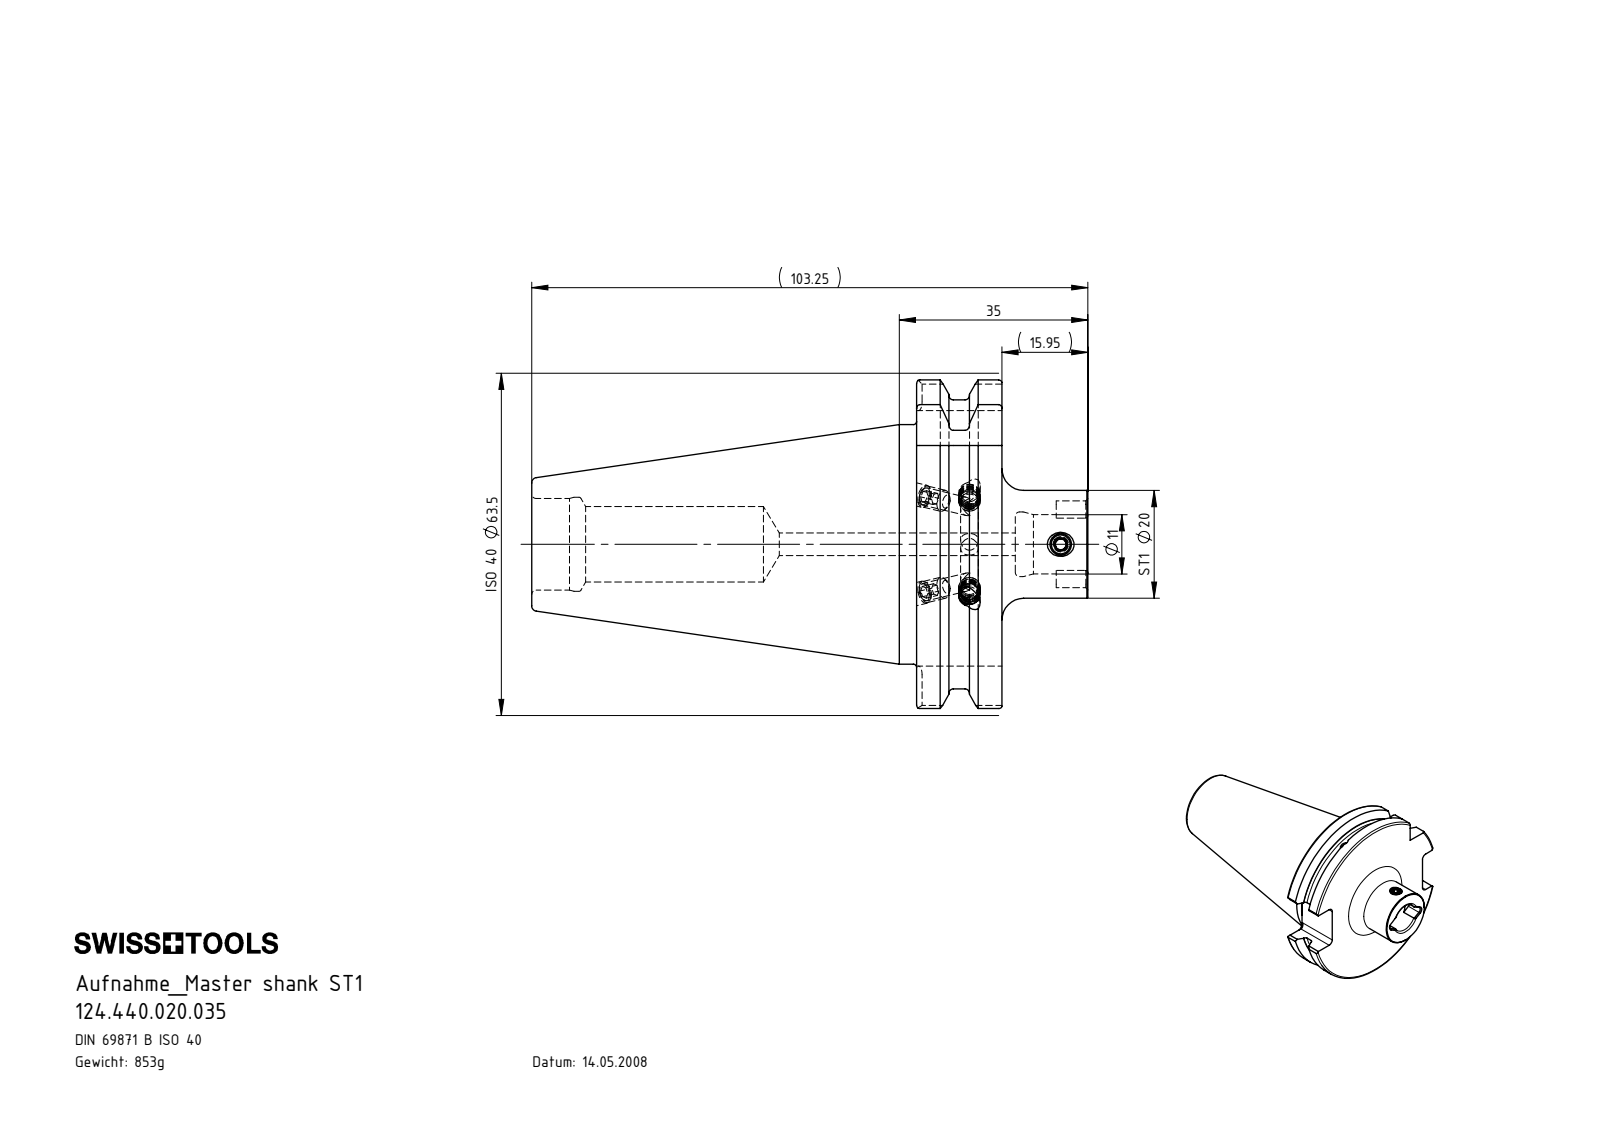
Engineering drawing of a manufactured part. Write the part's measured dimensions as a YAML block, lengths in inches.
part_name: "ISO 4026 - M4 x 5_PreviewCfg; SB4.ST1.K01.035; ST1-ER1.001.005_A; KVT_MB_600_040 (+1 more)"
step_written_by: "SolidWorks 2017 (AUTOMOTIVE_DESIGN)"
units: inches
bodies: {solids: 8, faces: 206, planar: 78, cylindrical: 50, other: 78}
overall_size: [4.065, 2.5, 2.399]
volume: 6.629
surface_area: 33.7
round_holes:
  - {diameter: 0.13, count: 3}
  - {diameter: 0.165, count: 3}
  - {diameter: 0.118, count: 2}
  - {diameter: 0.079, count: 1}
  - {diameter: 0.138, count: 1}
  - {diameter: 0.157, count: 1}
  - {diameter: 0.433, count: 1}
  - {diameter: 0.472, count: 1}
  - {diameter: 0.551, count: 1}
  - {diameter: 0.669, count: 1}
  - {diameter: 0.687, count: 1}
round_bosses_or_shafts:
  - {diameter: 0.157, count: 5}
  - {diameter: 1.75, count: 1}
  - {diameter: 0.787, count: 1}
partial_cylinders:
  - {radius: 0.063, count: 8}
  - {radius: 0.051, count: 2}
  - {radius: 1.102, count: 1}
  - {radius: 1.25, count: 1}
face_to_face_distances: [0.624, 1.866, 1.252, 0.628, 2.813, 3.437, 4.065, 0.634, 1.039, 0.406]
